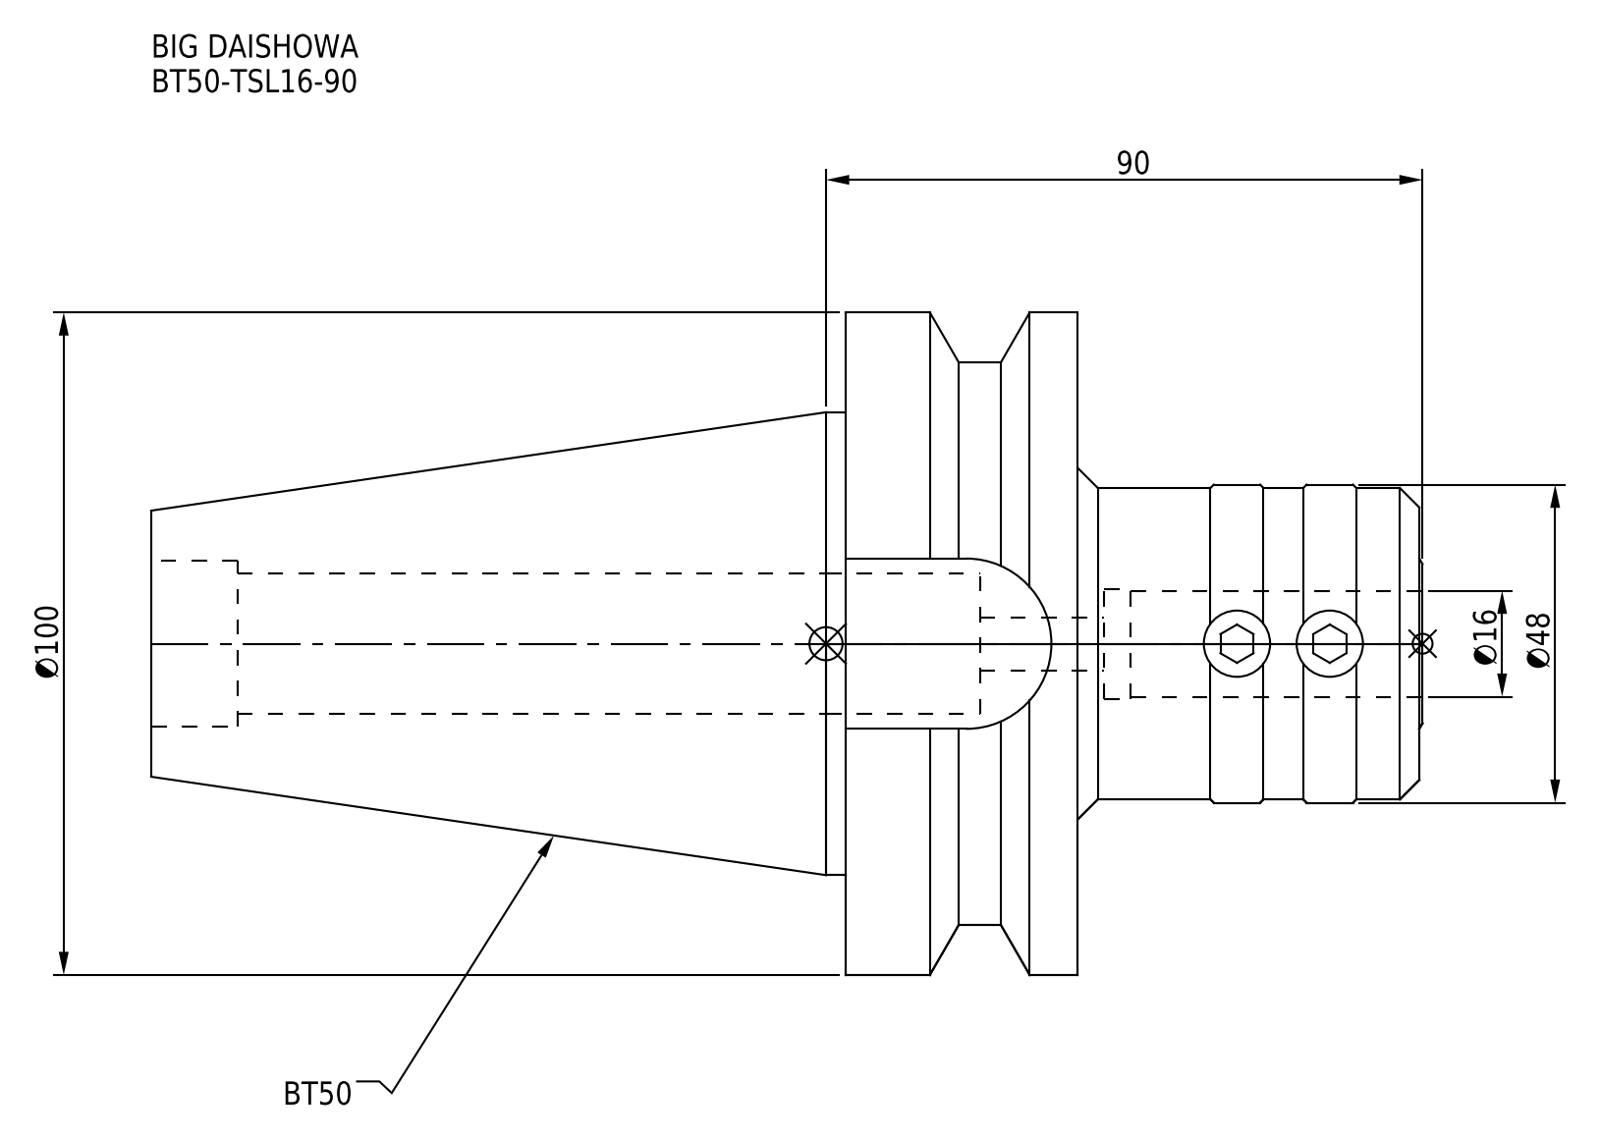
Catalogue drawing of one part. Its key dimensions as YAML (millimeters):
part_name: "BT50-TSL16-90"
step_written_by: "CREO PARAMETRIC BY PTC INC, 2016380 (AUTOMOTIVE_DESIGN)"
units: millimeters
bodies: {solids: 1, faces: 67, planar: 15, cylindrical: 32, other: 20}
overall_size: [191.8, 100, 100]
volume: 528254
surface_area: 63713
round_holes:
  - {diameter: 8, count: 1}
  - {diameter: 16, count: 1}
  - {diameter: 16.6, count: 1}
  - {diameter: 21.2, count: 1}
  - {diameter: 25, count: 1}
round_bosses_or_shafts:
  - {diameter: 100, count: 1}
  - {diameter: 85, count: 1}
  - {diameter: 69.85, count: 1}
  - {diameter: 48, count: 1}
  - {diameter: 47, count: 1}
partial_cylinders:
  - {radius: 12.85, count: 1}
face_to_face_distances: [35, 51.5, 86.5, 191.3, 139.8, 104.8, 70.8, 25.7, 66.3, 14.8]
